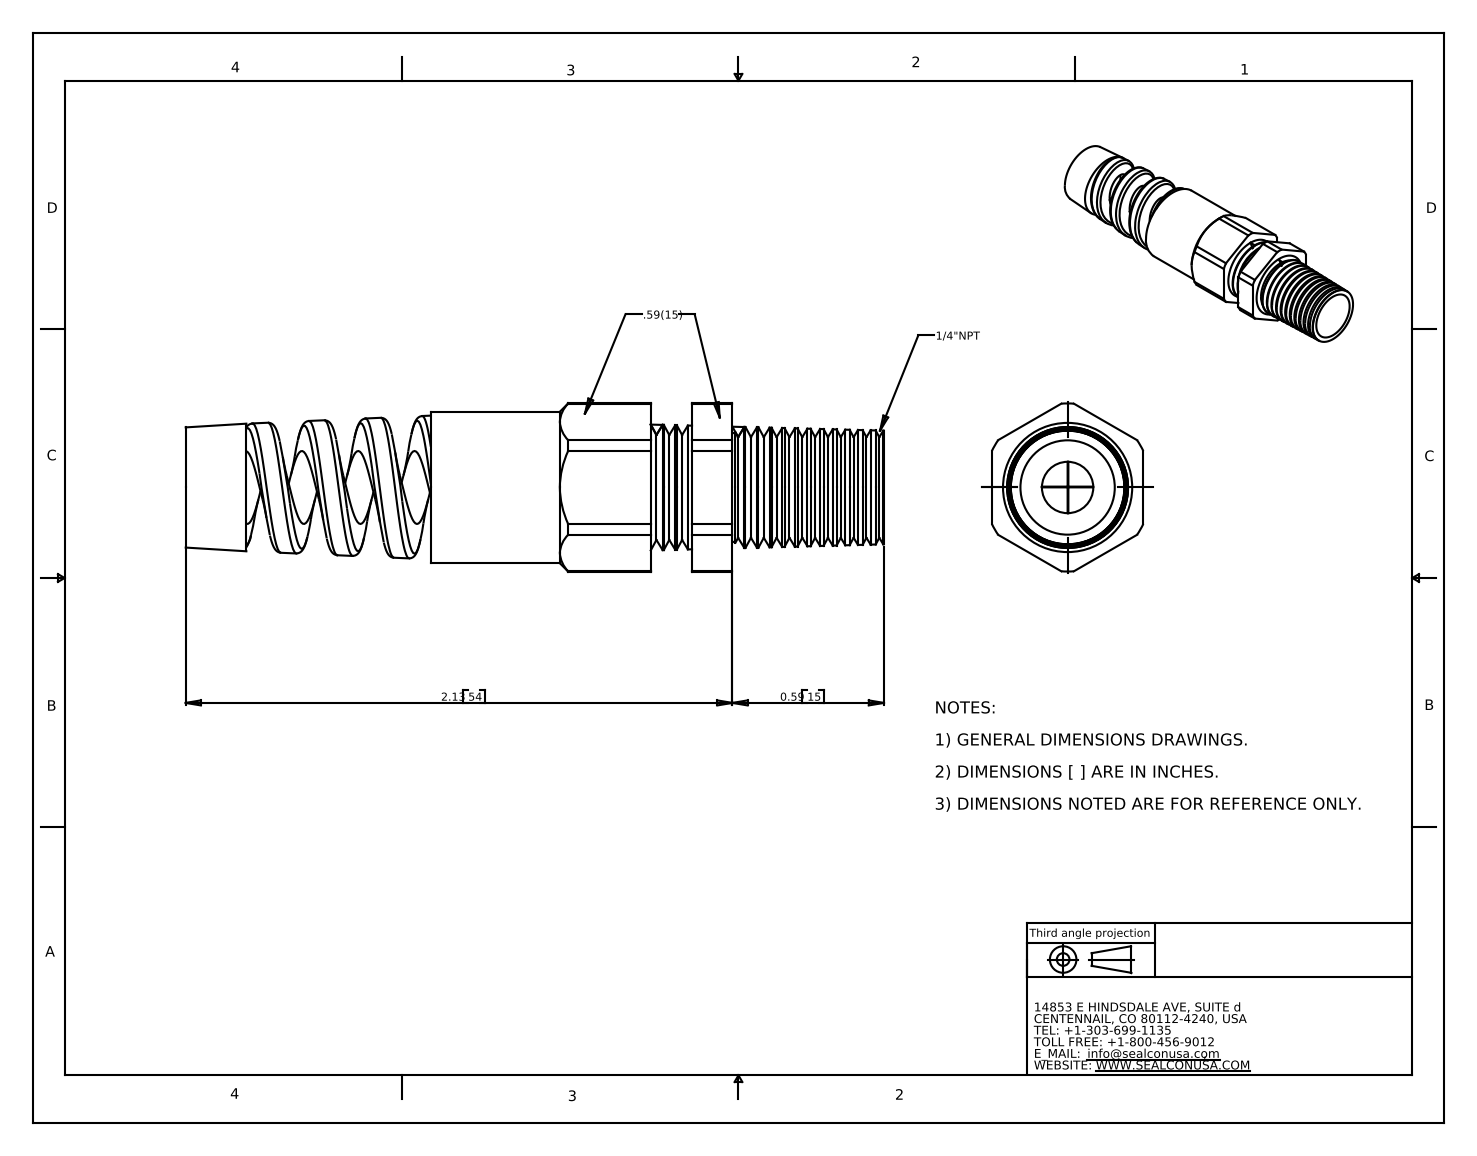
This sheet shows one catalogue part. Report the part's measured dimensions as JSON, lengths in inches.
{"part_name": "CF07CR-GY", "step_written_by": "SolidWorks 2007 (CONFIG_CONTROL_DESIGN)", "units": "inches", "bodies": {"solids": 2, "faces": 177, "planar": 24, "cylindrical": 33, "other": 120}, "overall_size": [2.72, 0.655, 0.59], "volume_in3": 0.387, "surface_area_in2": 8.877, "round_holes": [[0.2, 1], [0.284, 1], [0.313, 1]], "round_bosses_or_shafts": [[0.59, 1], [0.367, 1]], "partial_cylinders_radius": [[0.327, 1]], "face_to_face_distances": [0.59, 0.515, 0.502, 1.018, 0.157, 0.673, 0.857, 0.354, 0.161, 1.175]}
